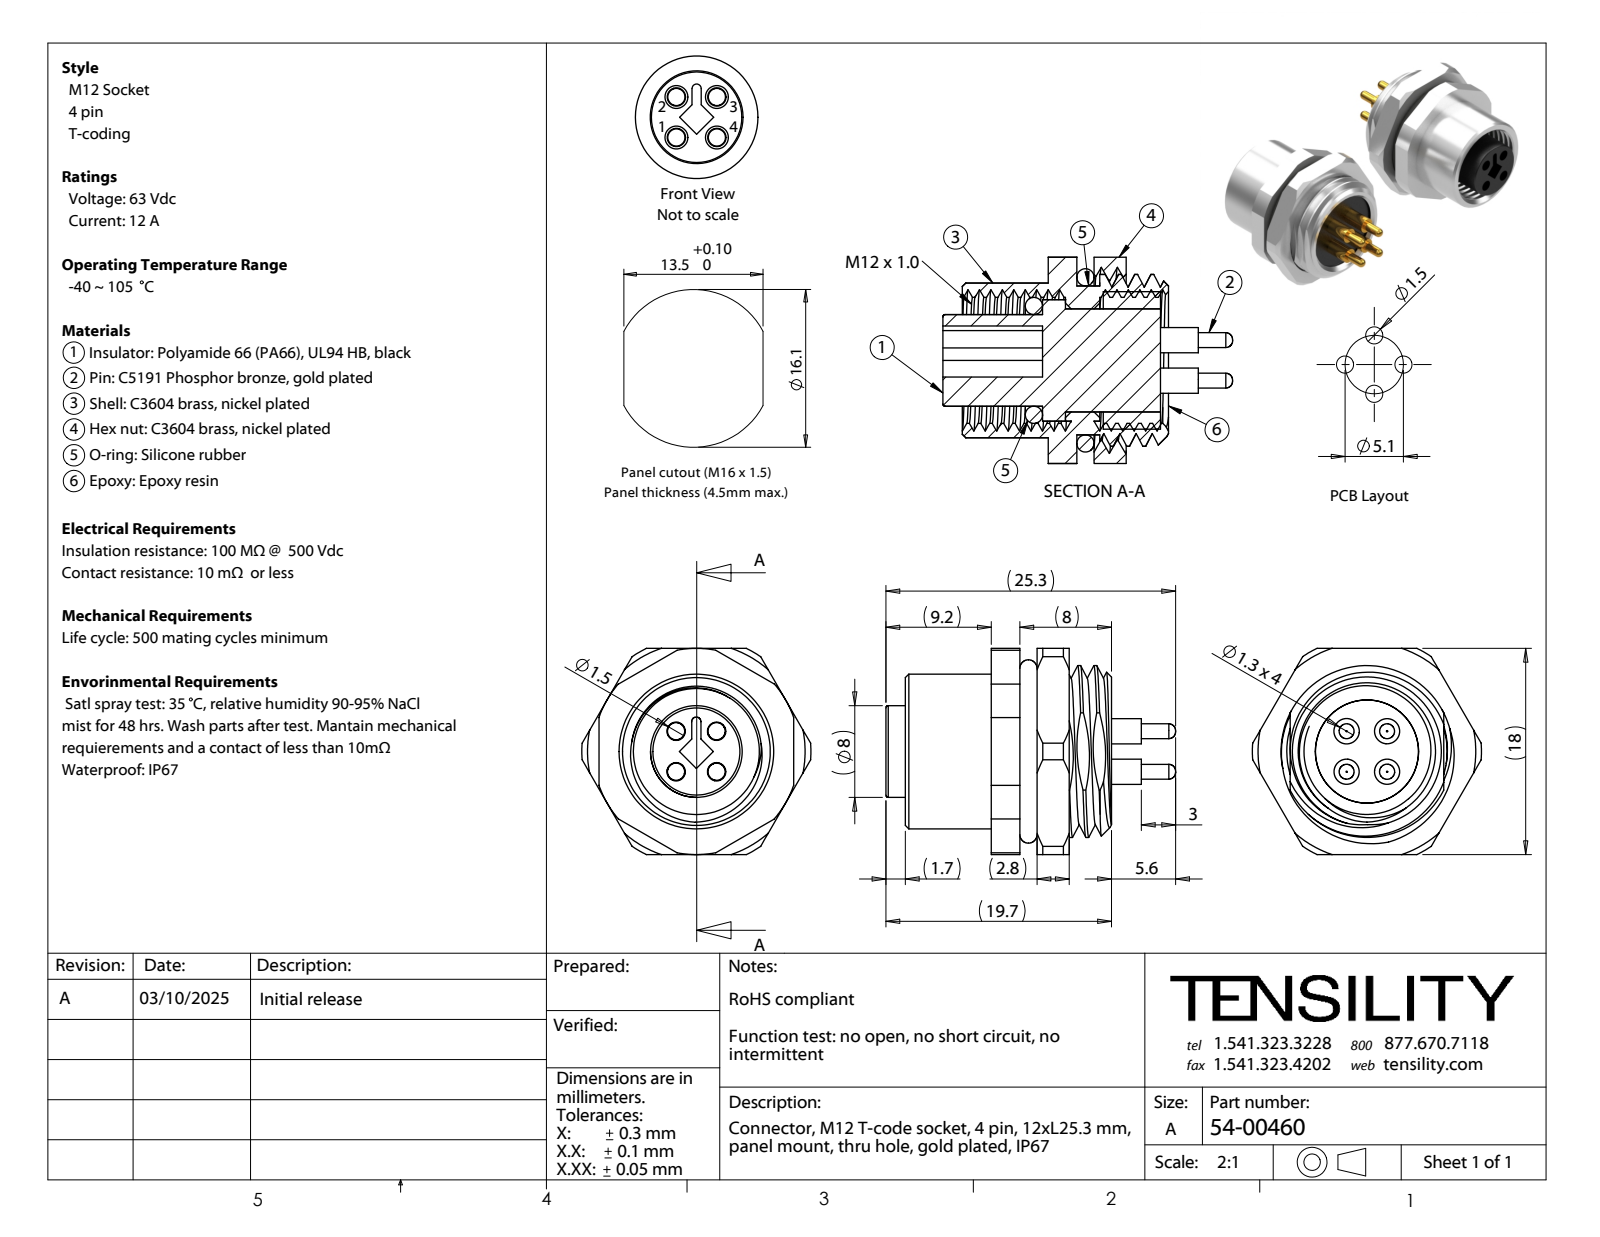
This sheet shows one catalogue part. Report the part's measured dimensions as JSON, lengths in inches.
{"part_name": "54-00460-05; 54-00460-02; 54-00460-01; 54-00460-03 (+3 more)", "step_written_by": "SolidWorks 2021 (CONFIG_CONTROL_DESIGN)", "units": "inches", "bodies": {"solids": 10, "faces": 314, "planar": 98, "cylindrical": 132, "other": 84}, "overall_size": [0.996, 0.787, 0.709], "volume_in3": 0.172, "surface_area_in2": 9.083, "round_holes": [[0.059, 4], [0.063, 4], [0.354, 1], [0.433, 1], [0.551, 1]], "round_bosses_or_shafts": [[0.087, 4], [0.051, 4], [0.531, 1], [0.512, 1], [0.472, 1], [0.417, 1], [0.315, 1]], "partial_cylinders_radius": [[0.016, 1], [0.295, 1], [0.354, 1], [0.394, 1]], "face_to_face_distances": [0.118, 0.098, 0.287, 0.079, 0.059, 0.209, 0.386, 0.157, 0.197, 0.091], "hole_center_spacings": [0.098, 0.139, 0.197]}
